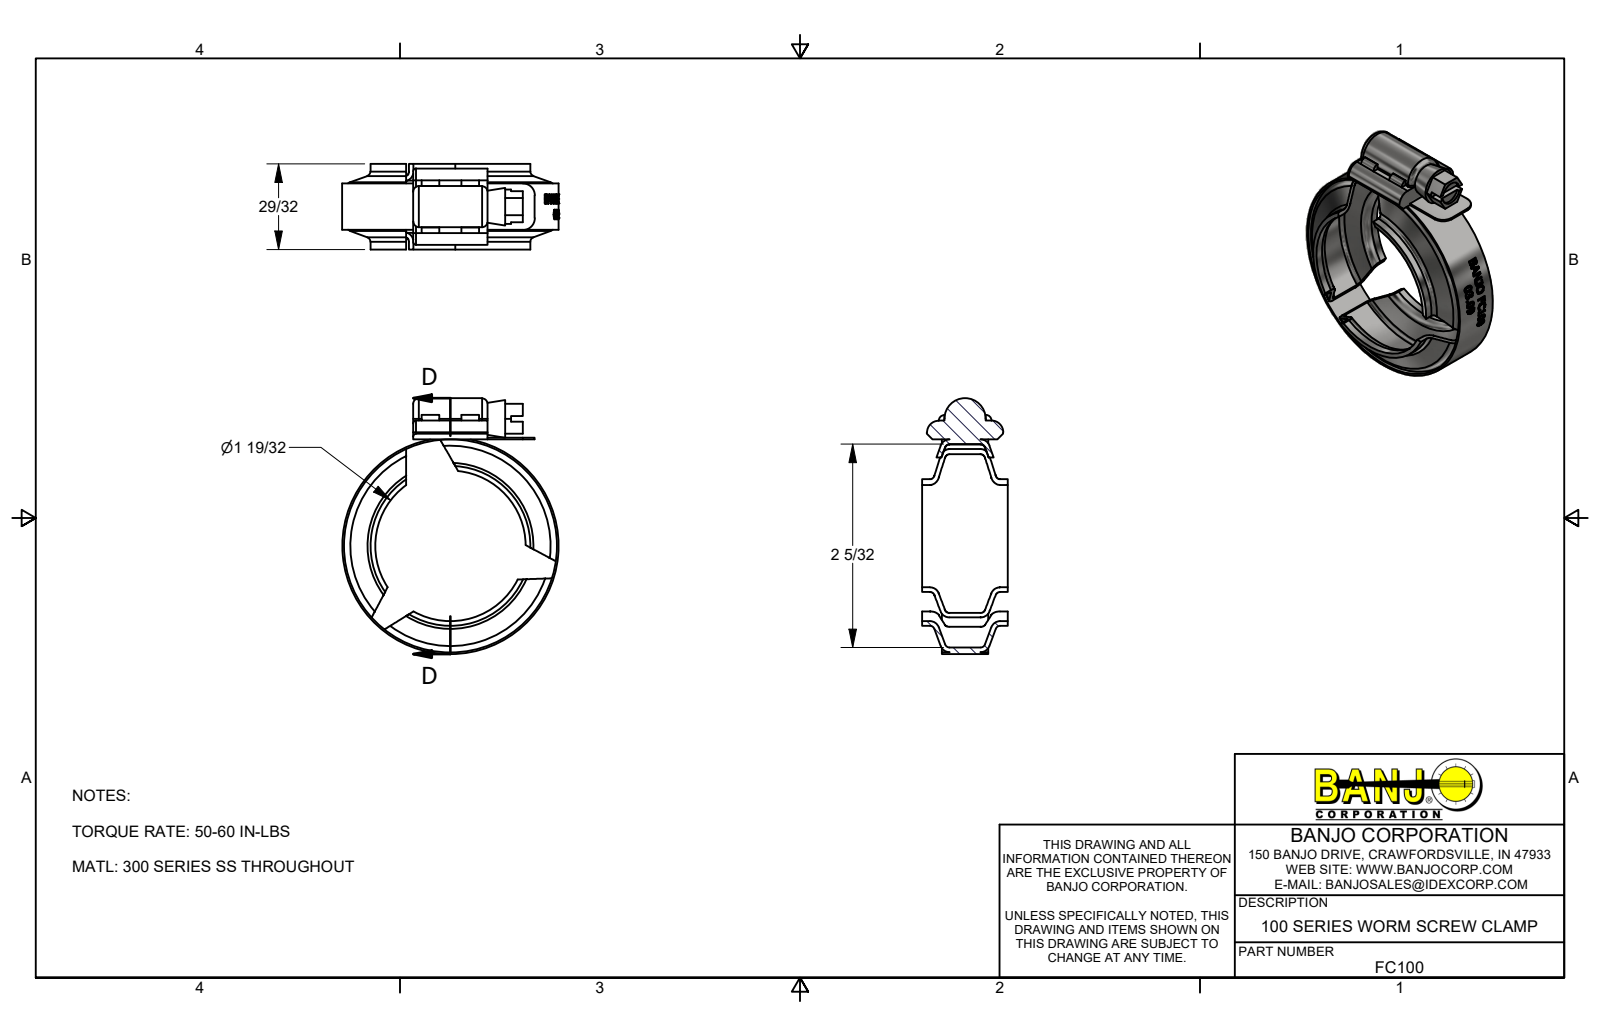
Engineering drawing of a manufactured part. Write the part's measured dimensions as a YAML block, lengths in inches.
part_name: "FC100"
step_written_by: "Autodesk Inventor 2013 (AUTOMOTIVE_DESIGN)"
units: inches
bodies: {solids: 1, faces: 380, planar: 135, cylindrical: 58, other: 187}
overall_size: [2.717, 2.299, 0.91]
volume: 0.614
surface_area: 19.7
round_holes:
  - {diameter: 0.25, count: 1}
  - {diameter: 2.16, count: 1}
  - {diameter: 2.26, count: 1}
round_bosses_or_shafts:
  - {diameter: 2.299, count: 1}
partial_cylinders:
  - {radius: 0.06, count: 4}
  - {radius: 0.125, count: 4}
  - {radius: 0.03, count: 3}
  - {radius: 0.219, count: 1}
  - {radius: 0.799, count: 1}
  - {radius: 0.849, count: 1}
  - {radius: 1.14, count: 1}
face_to_face_distances: [0.209, 0.701, 0.02, 0.91, 0.492, 0.79, 0.317, 0.865, 0.075, 0.188]
